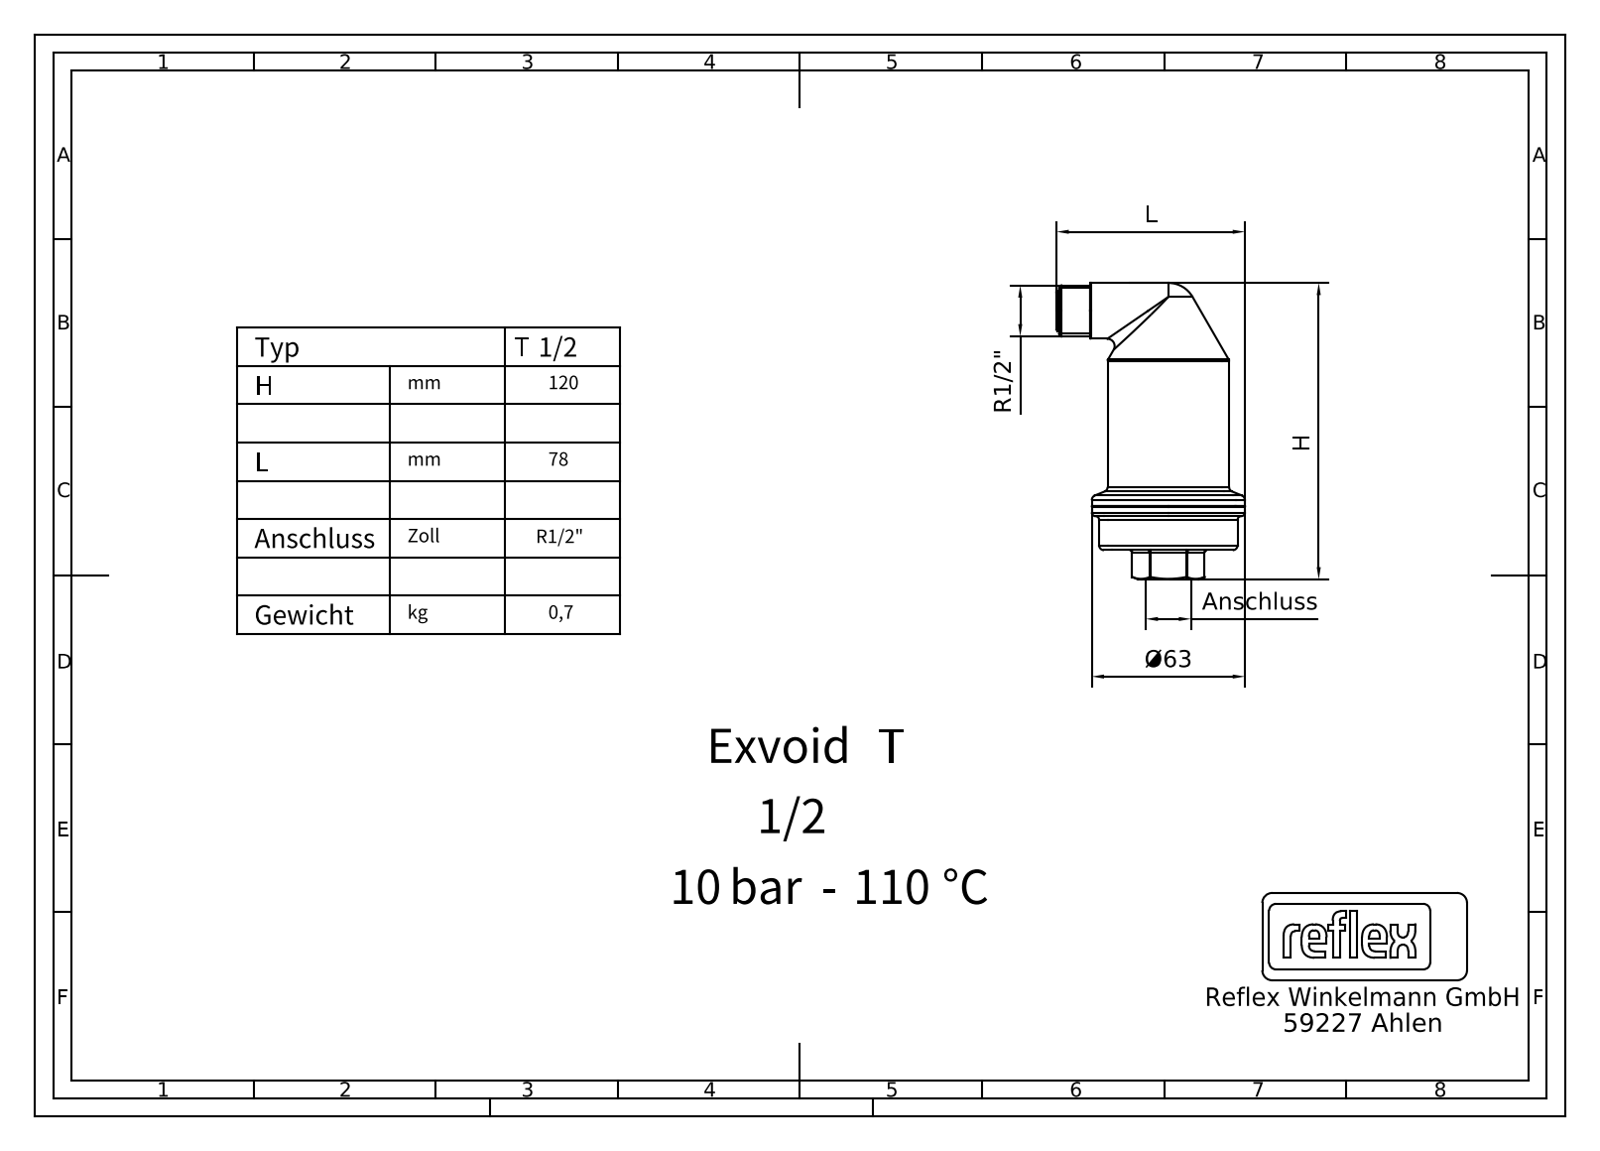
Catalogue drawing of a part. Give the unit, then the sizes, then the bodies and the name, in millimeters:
Units: millimetres
Overall size (bounding box): 122 × 77.5 × 63
Round holes (diameter × count): ⌀10 ×3, ⌀1.05 ×1, ⌀1.5 ×1, ⌀2 ×1, ⌀3.2 ×1, ⌀14.95 ×1, ⌀18.63 ×1, ⌀45 ×1, ⌀46.3 ×1, ⌀48 ×1, ⌀50.79 ×1, ⌀61 ×1
Round bosses / shafts (diameter × count): ⌀1 ×4, ⌀63 ×1, ⌀57 ×1, ⌀55.3 ×1, ⌀53.75 ×1, ⌀50 ×1, ⌀46 ×1, ⌀40 ×1
Partial cylindrical surfaces — rounded edges, fillets, slot ends (radius × count): R0.1 ×18, R1 ×14, R0.5 ×6, R7.4 ×2, R4 ×1, R6 ×1
Main face-to-face distances: 8, 2.5, 6.3, 8.8, 5.5, 0.8, 18, 10, 15.5, 9.2
Hole centre spacings: 12.4, 21.48
Volume: 108 441 mm³ · Surface area: 65 354 mm²
Bodies: 13 solids, 444 faces (54 planar, 155 cylindrical, 235 other)
Part name (STEP PRODUCT): REF-000921_BL00_V00; REF-000919_BL00_V00; REF-000841_BL00_V00; REF-000840_BL00_V00 (+8 more)
STEP written by: CATIA V5 STEP AP214 (AUTOMOTIVE_DESIGN)
